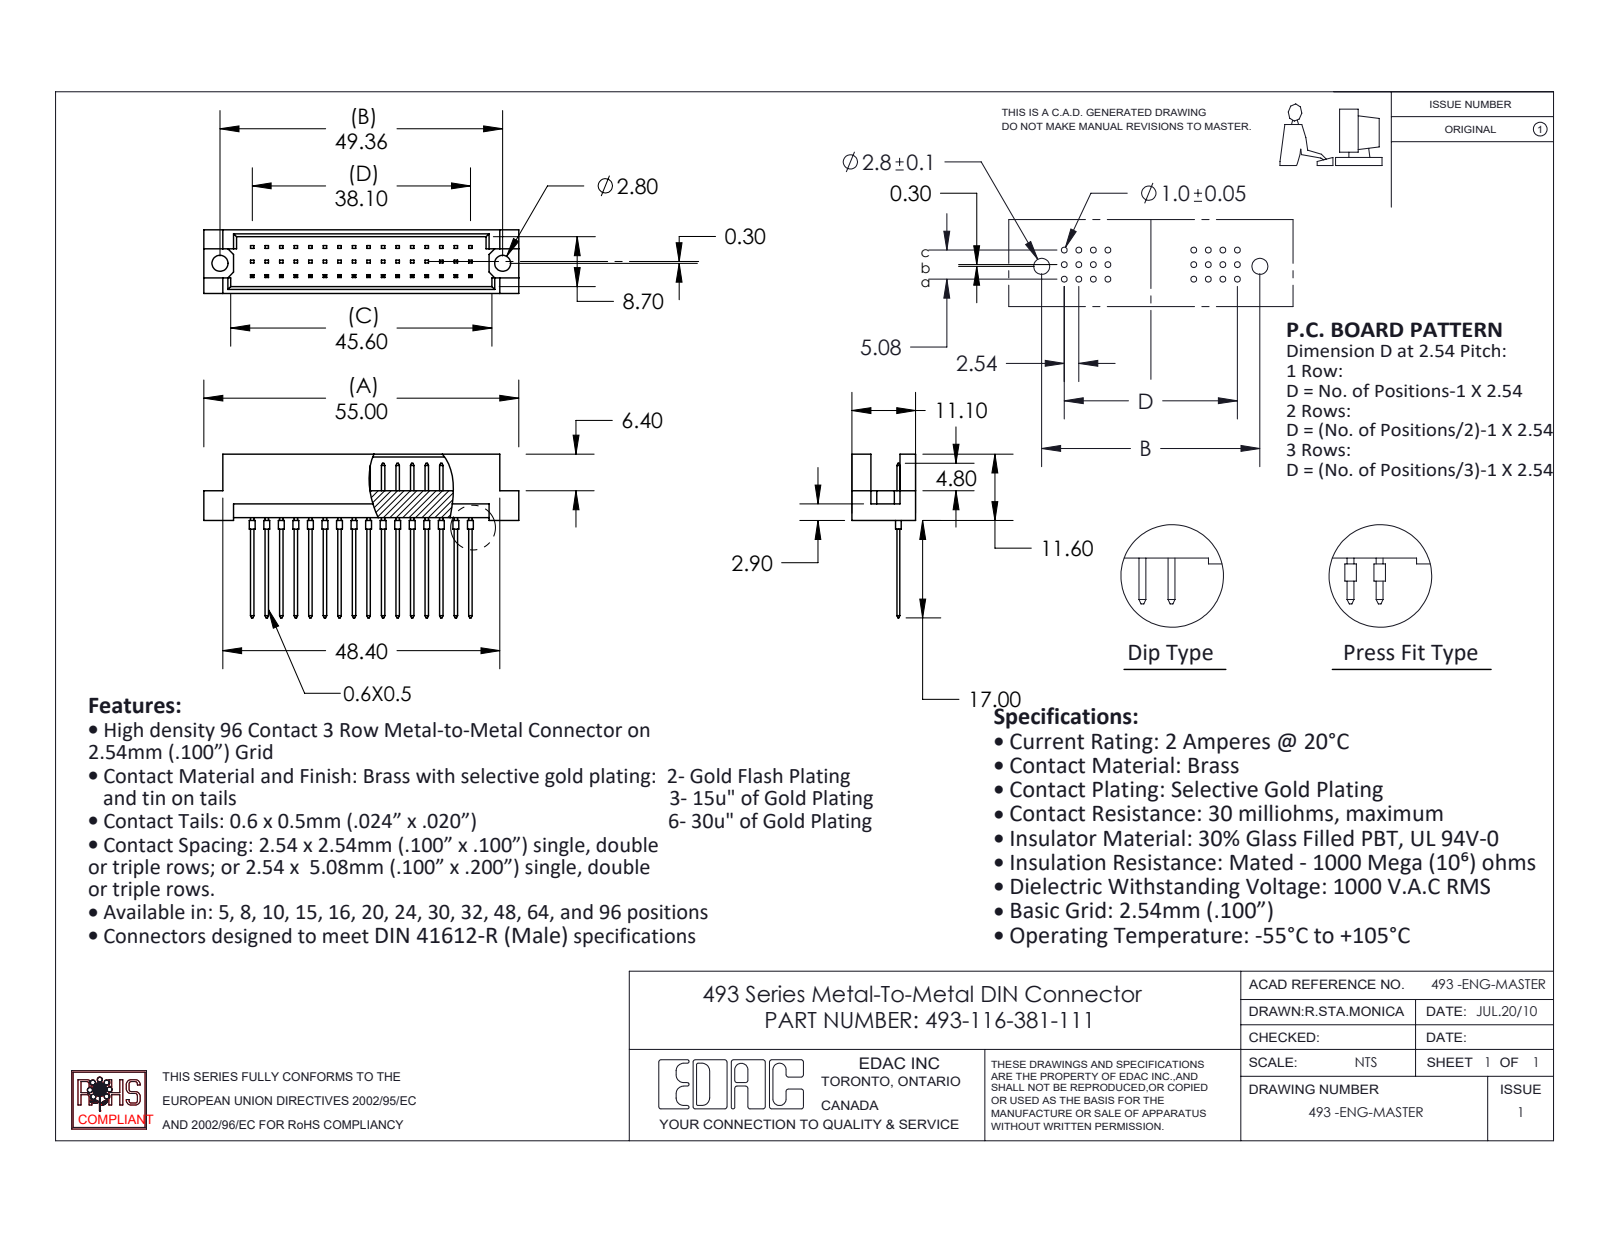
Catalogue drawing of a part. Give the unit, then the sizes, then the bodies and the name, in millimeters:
Units: millimetres
Overall size (bounding box): 55 × 28.6 × 11.1
Round holes (diameter × count): ⌀2.8 ×2
Round bosses / shafts (diameter × count): ⌀1 ×16
Main face-to-face distances: 1.2, 9.9, 11.1, 0.5, 2.54, 8.7, 5.08, 4.7, 2.76, 8.34
Hole centre spacings: 49.36
Volume: 3 412 mm³ · Surface area: 4 739 mm²
Bodies: 17 solids, 596 faces (560 planar, 36 cylindrical, 0 other)
Part name (STEP PRODUCT): 493-116-381-111; 493 Part_48; 493-290_81
STEP written by: SolidWorks 2020 (CONFIG_CONTROL_DESIGN)
